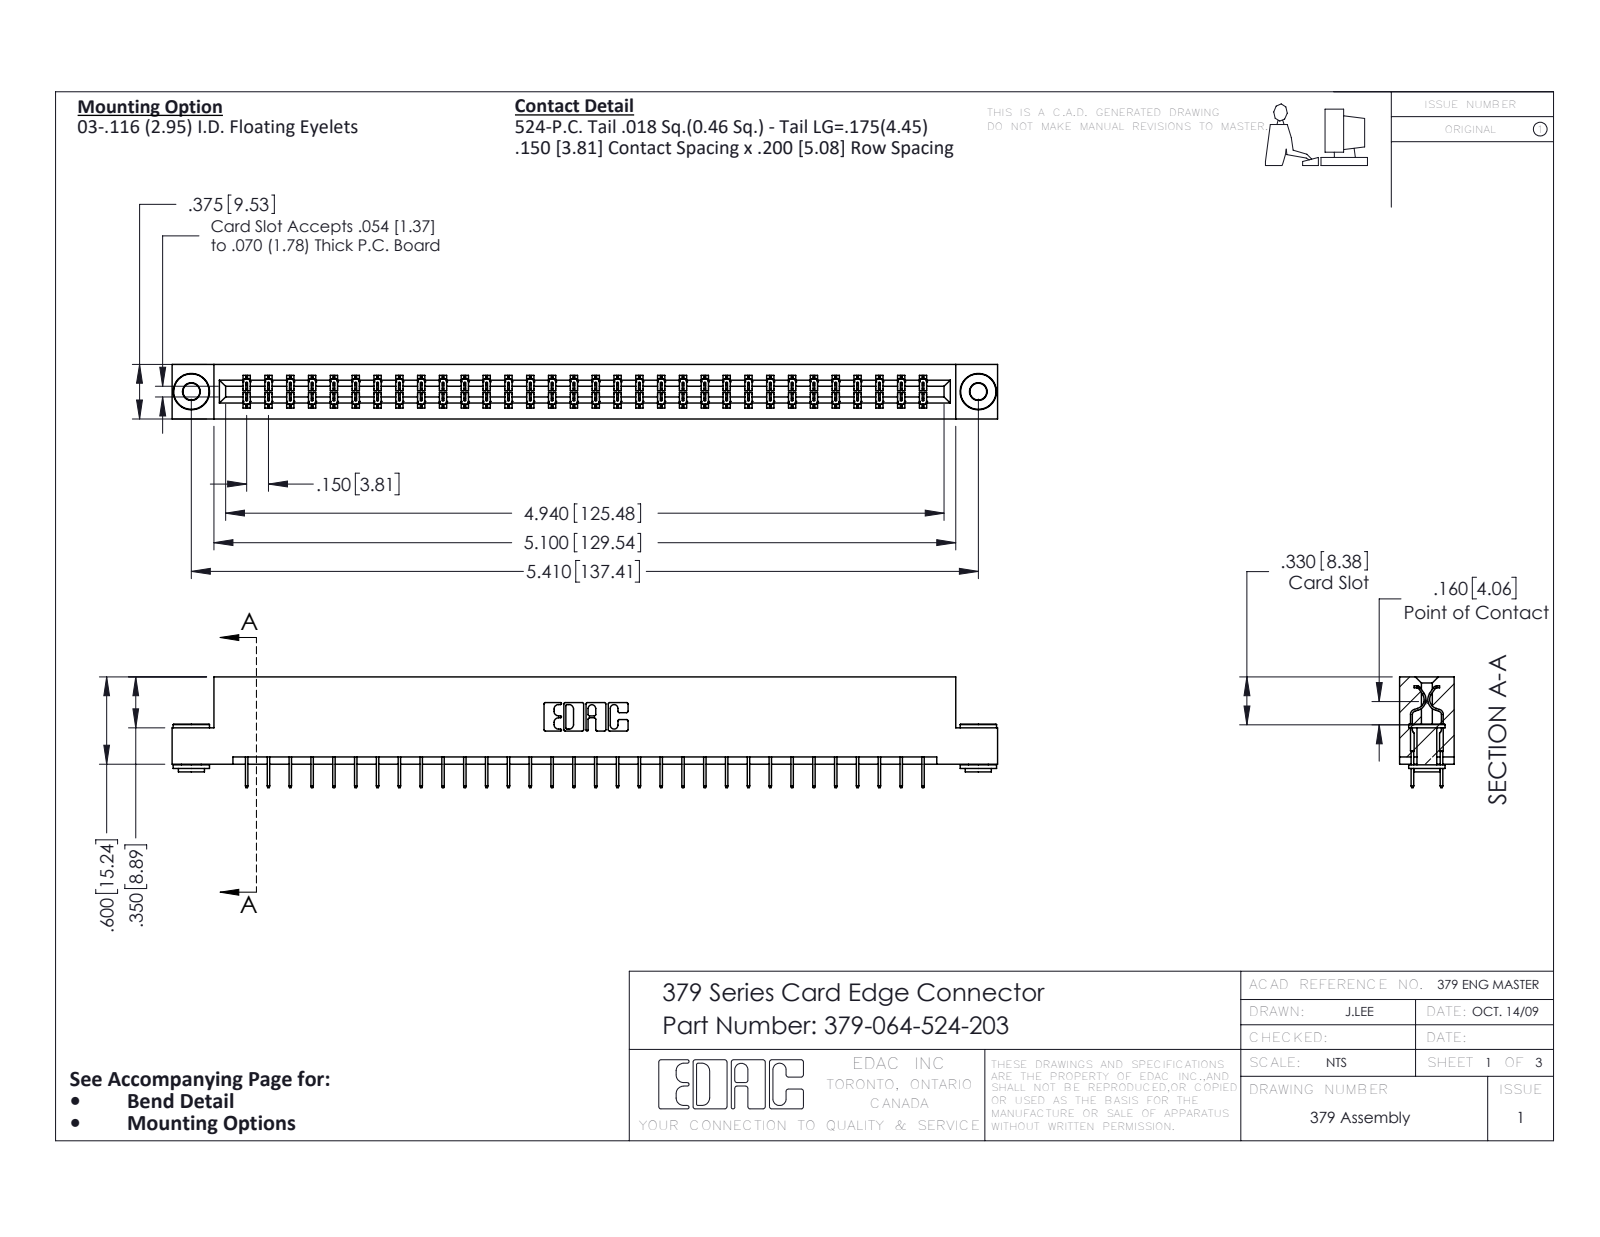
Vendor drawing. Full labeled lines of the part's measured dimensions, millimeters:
Part name (STEP PRODUCT): 345-292-001_345-293-124; 345-250-002_345-250-002-102; 379-064-524-203; 379 Part_Flush - .156 Dia - TH
STEP written by: SolidWorks 2016 (CONFIG_CONTROL_DESIGN)
Units: millimetres
Bodies: 67 solids, 3736 faces (2768 planar, 960 cylindrical, 8 other)
Overall size (bounding box): 144.1 × 19.4 × 9.5
Volume: 15 200 mm³ · Surface area: 16 860 mm²
Round holes (diameter × count): ⌀2.9 ×2, ⌀4 ×2
Round bosses / shafts (diameter × count): ⌀6.4 ×2, ⌀4.6 ×2, ⌀3.5 ×2
Partial cylindrical surfaces — rounded edges, fillets, slot ends (radius × count): R0.2 ×96, R0.3 ×22, R0.2 ×6, R0.8 ×6, R0.7 ×3, R0.4 ×2, R0.6 ×2, R0.6 ×2
Main face-to-face distances: 7.6, 1.9, 9.5, 5.1, 5.7, 2.5, 14, 3.8, 1.9, 7
Hole centre spacings: 137.4
